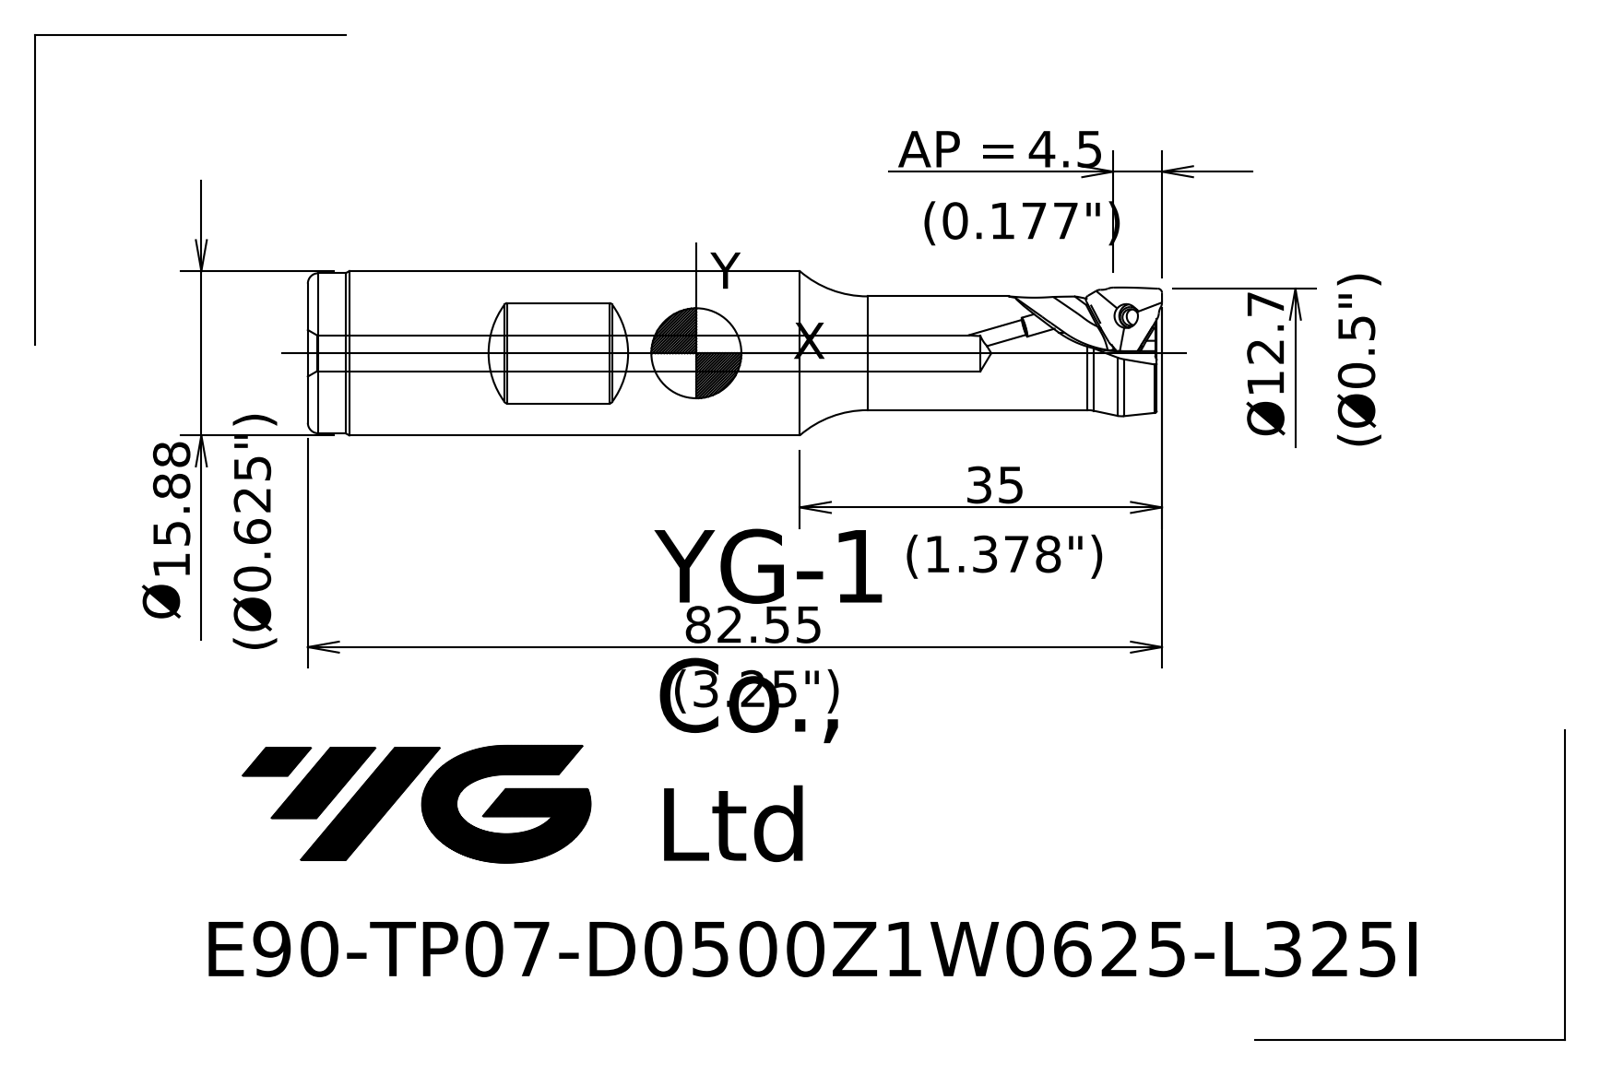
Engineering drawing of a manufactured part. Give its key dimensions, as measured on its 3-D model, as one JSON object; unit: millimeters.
{"part_name": "102214542B34yi50", "step_written_by": "SIEMENS PLM Software NX 10.0 (AP203_CONFIGURATION_CONTROLLED_3D_DESIGN_OF_MECHANICAL_PARTS_AND_ASSEMBLIES_MIM_LF)", "units": "millimeters", "bodies": {"solids": 1, "faces": 45, "planar": 6, "cylindrical": 6, "other": 33}, "overall_size": [82.55, 15.88, 15.88], "volume_mm3": 12156, "surface_area_mm2": 5155, "round_holes": [[3.5, 1]], "round_bosses_or_shafts": [[15.88, 1], [15.47, 1], [11, 1]], "partial_cylinders_radius": [[0.3, 2]], "face_to_face_distances": [81.9, 82.05]}
